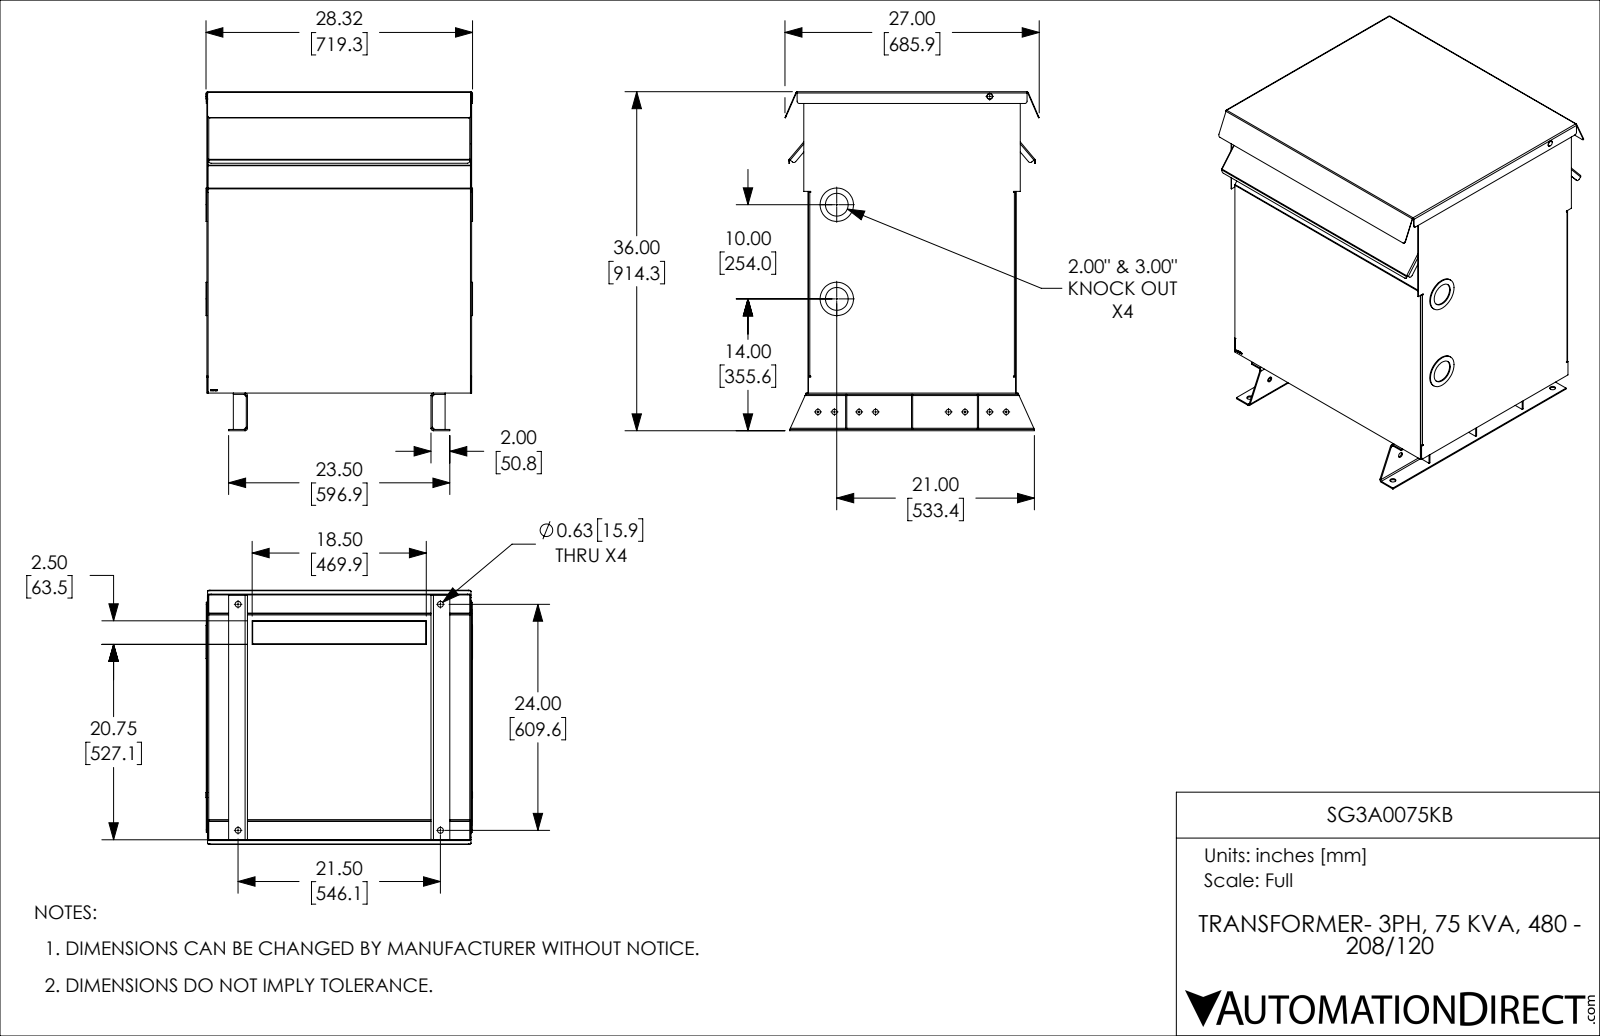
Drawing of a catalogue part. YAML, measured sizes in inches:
part_name: "SG3A0075KB"
step_written_by: "SolidWorks 2018 (AUTOMOTIVE_DESIGN)"
units: inches
bodies: {solids: 16, faces: 562, planar: 340, cylindrical: 174, other: 48}
overall_size: [35.997, 28.32, 27.005]
volume: 369.5
surface_area: 11392
round_holes:
  - {diameter: 0.563, count: 8}
  - {diameter: 0.625, count: 4}
  - {diameter: 2.415, count: 2}
  - {diameter: 0.625, count: 1}
round_bosses_or_shafts:
  - {diameter: 3.545, count: 2}
  - {diameter: 0.563, count: 1}
partial_cylinders:
  - {radius: 0.075, count: 28}
  - {radius: 0.135, count: 28}
  - {radius: 0.25, count: 14}
  - {radius: 0.125, count: 4}
  - {radius: 0.259, count: 4}
face_to_face_distances: [0.06, 28.06, 31.937, 22.06, 22, 28, 28.12, 31.997, 22.12, 31.878]
hole_center_spacings: [1.75, 4.375, 13.875, 2.625, 6.125, 9.5, 12.125, 15.625]
